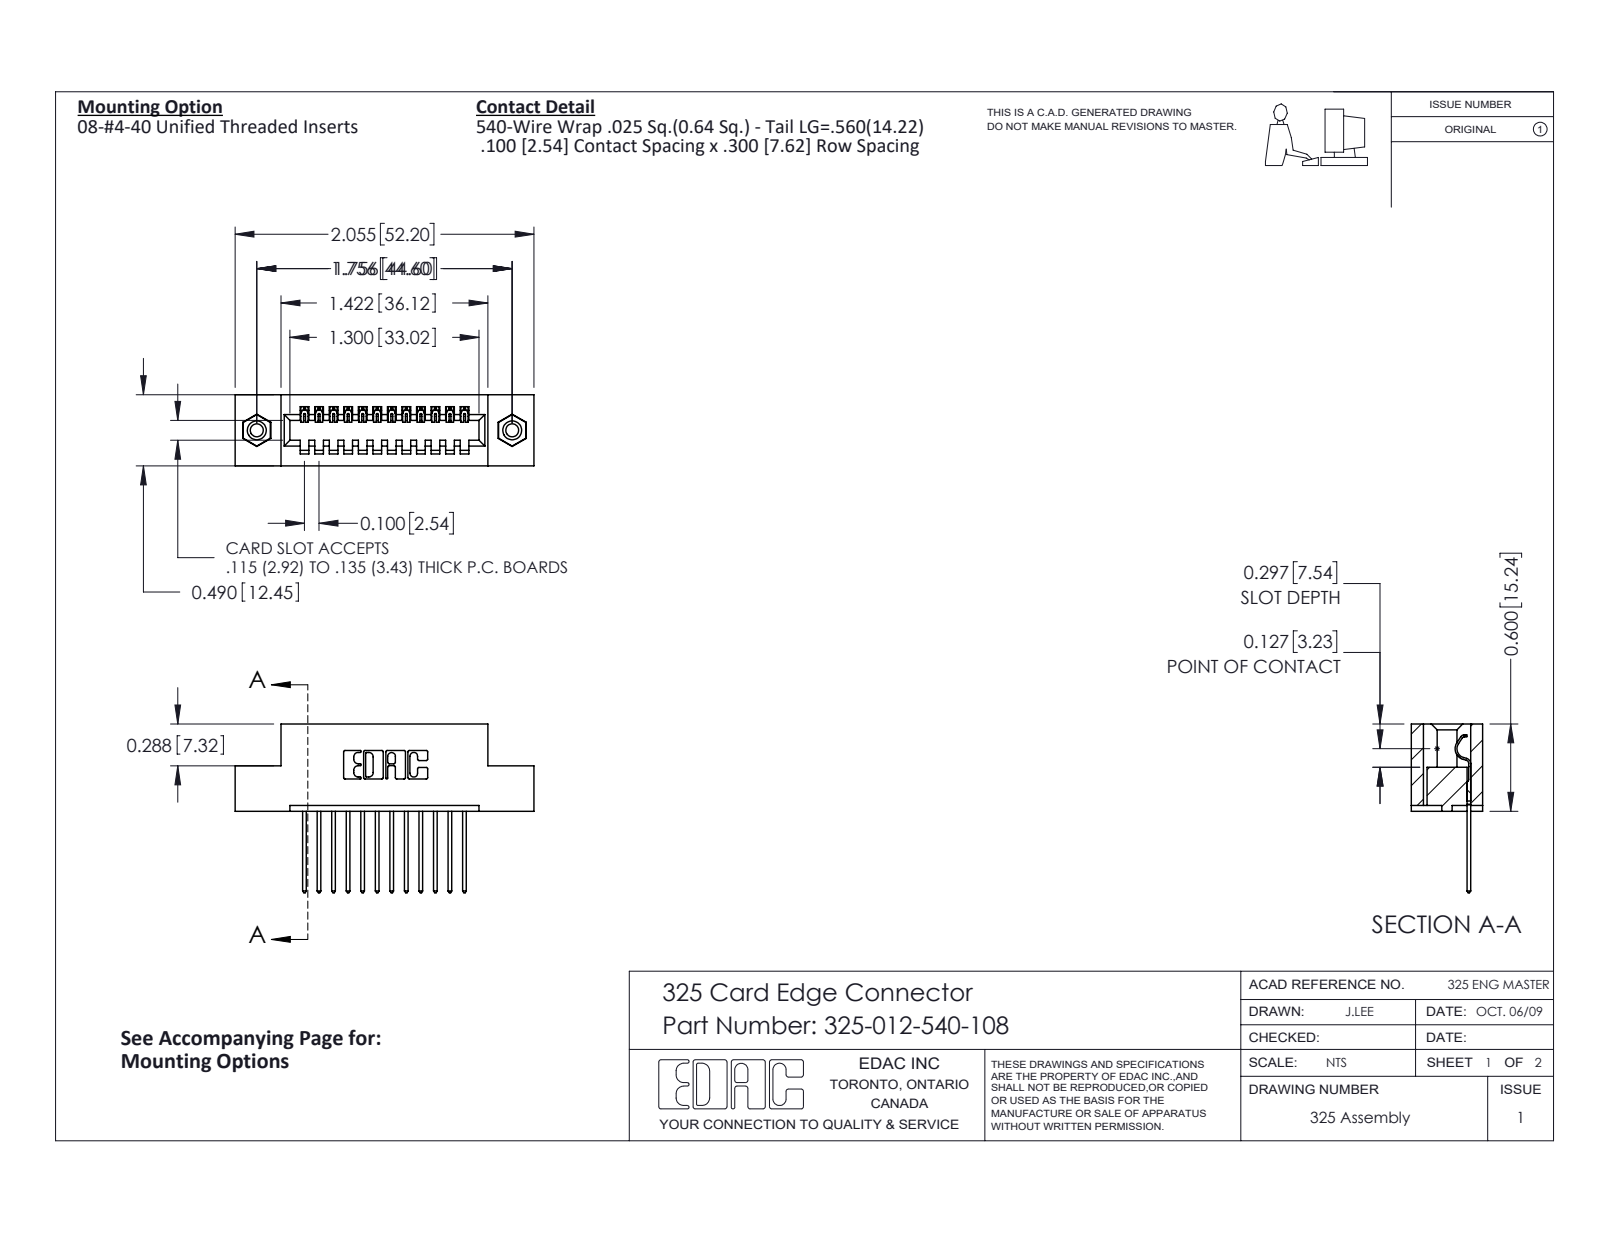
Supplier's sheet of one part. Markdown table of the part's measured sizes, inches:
| quantity | value |
| --- | --- |
| part name | 325-012-540-108; 325-292-001_325-293-140; 325 Part_TI; 345-250-001_345-250-003-102 |
| STEP written by | SolidWorks 2016 (CONFIG_CONTROL_DESIGN) |
| units | inches |
| bodies | 15 solids, 870 faces (606 planar, 248 cylindrical, 16 other) |
| overall size | 2.055 × 1.16 × 0.49 |
| volume | 0.391 in³ |
| surface area | 10.26 in² |
| round holes (diameter × count) | 0.089 × 2, 0.125 × 2, 0.16 × 2 |
| round bosses / shafts (diameter × count) | 0.155 × 2 |
| partial cylindrical surfaces (radius × count) | 0.006 × 24, 0.01 × 24, 0.01 × 22, 0.007 × 6, 0.031 × 6, 0.026 × 3, 0.014 × 1, 0.022 × 1 |
| main face-to-face distances | 0.083, 0.407, 0.3, 0.49, 0.04, 0.1, 0.2, 0.6, 0.107, 0.383 |
| hole center spacings | 1.756 |
